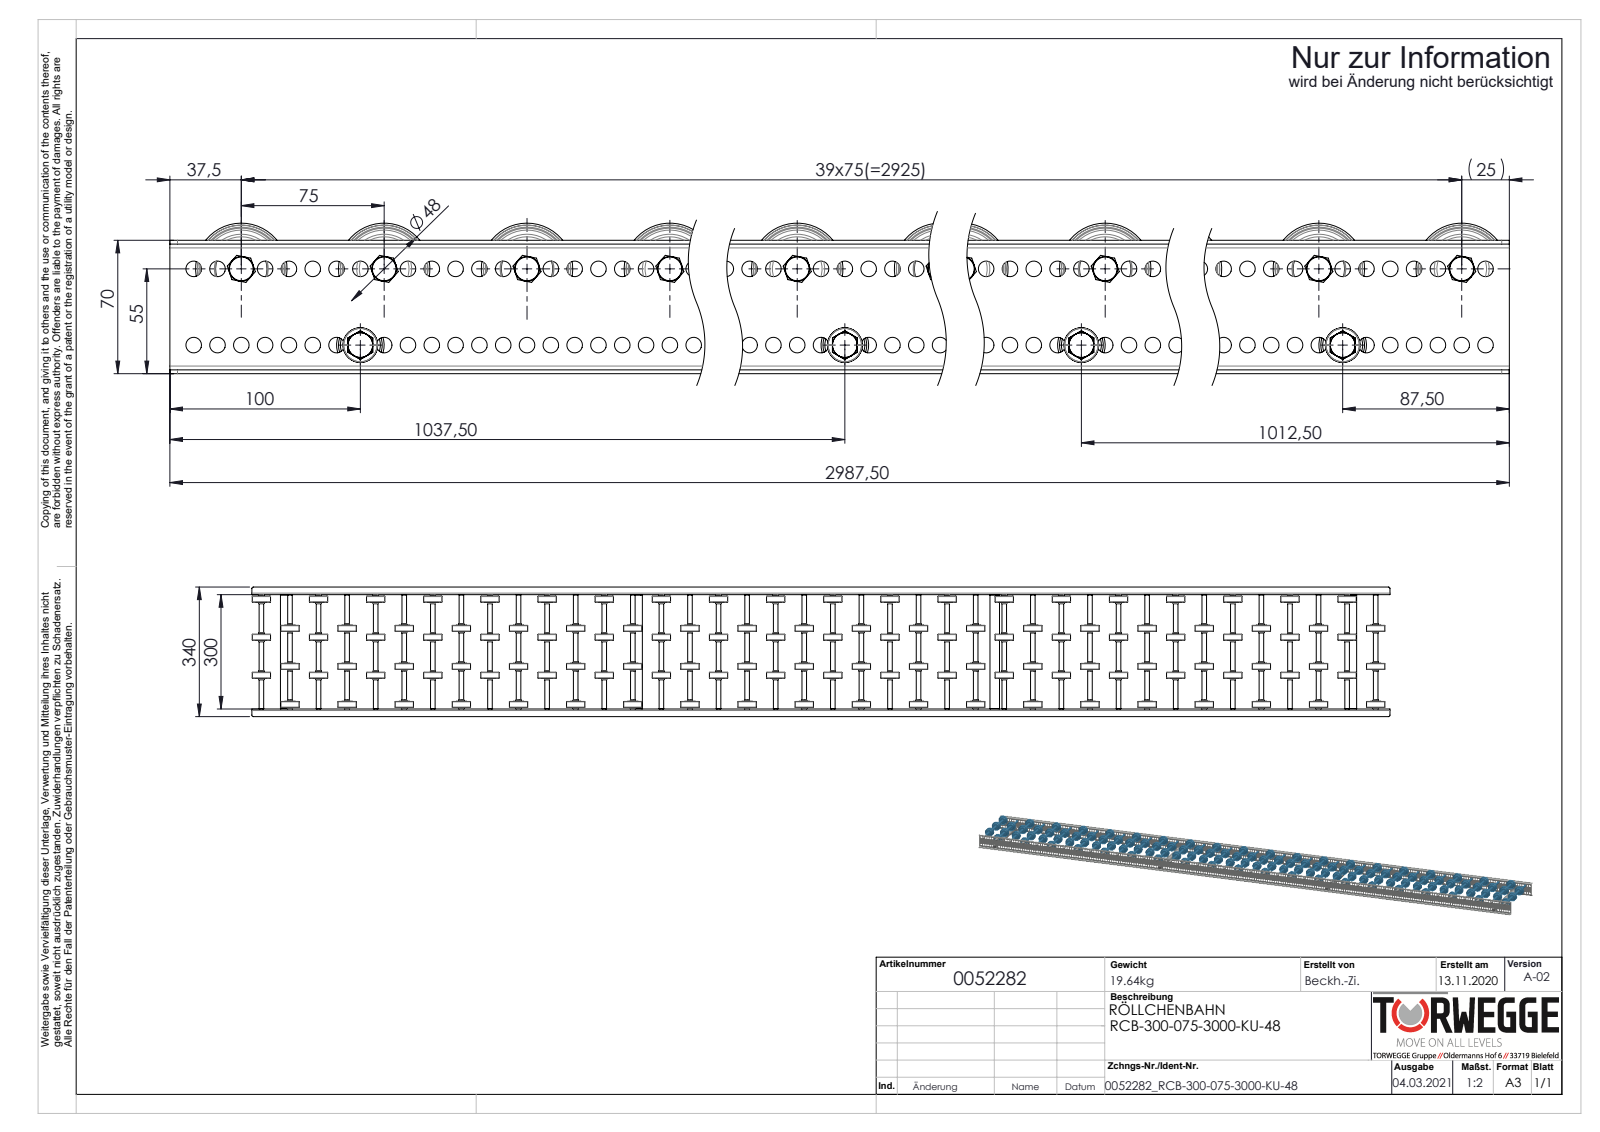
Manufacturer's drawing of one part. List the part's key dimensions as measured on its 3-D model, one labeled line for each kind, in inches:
Part name (STEP PRODUCT): Röllchenachse-für-Konfiguration_EL300; S100994_Sperrzahnschraube_M08x16-8.8-A2K; 0052282; S106837_Gewindestange-M8-KFG_L320 (+5 more)
STEP written by: SolidWorks 2020 (AUTOMOTIVE_DESIGN)
Units: inches
Bodies: 382 solids, 13972 faces (2484 planar, 5040 cylindrical, 6448 other)
Overall size (bounding box): 117.618 × 13.386 × 3.11
Volume: 289.6 in³ · Surface area: 5 561 in²
Round holes (diameter × count): ⌀0.323 ×476, ⌀0.262 ×40, ⌀0.38 ×40, ⌀0.539 ×40, ⌀0.268 ×4, ⌀0.827 ×4
Round bosses / shafts (diameter × count): ⌀0.315 ×44, ⌀1.89 ×40, ⌀1.063 ×40, ⌀0.5 ×40, ⌀0.492 ×40, ⌀0.472 ×40, ⌀0.984 ×4
Partial cylindrical surfaces — rounded edges, fillets, slot ends (radius × count): R0.157 ×8, R0.079 ×4
Main face-to-face distances: 0.079, 11.89, 2.677, 11.811, 11.969, 2.756, 2.598, 3.929, 0.642, 2.996
Hole centre spacings: 0.492, 0.984, 1.476, 1.969, 2.461, 2.953, 3.445, 3.937
